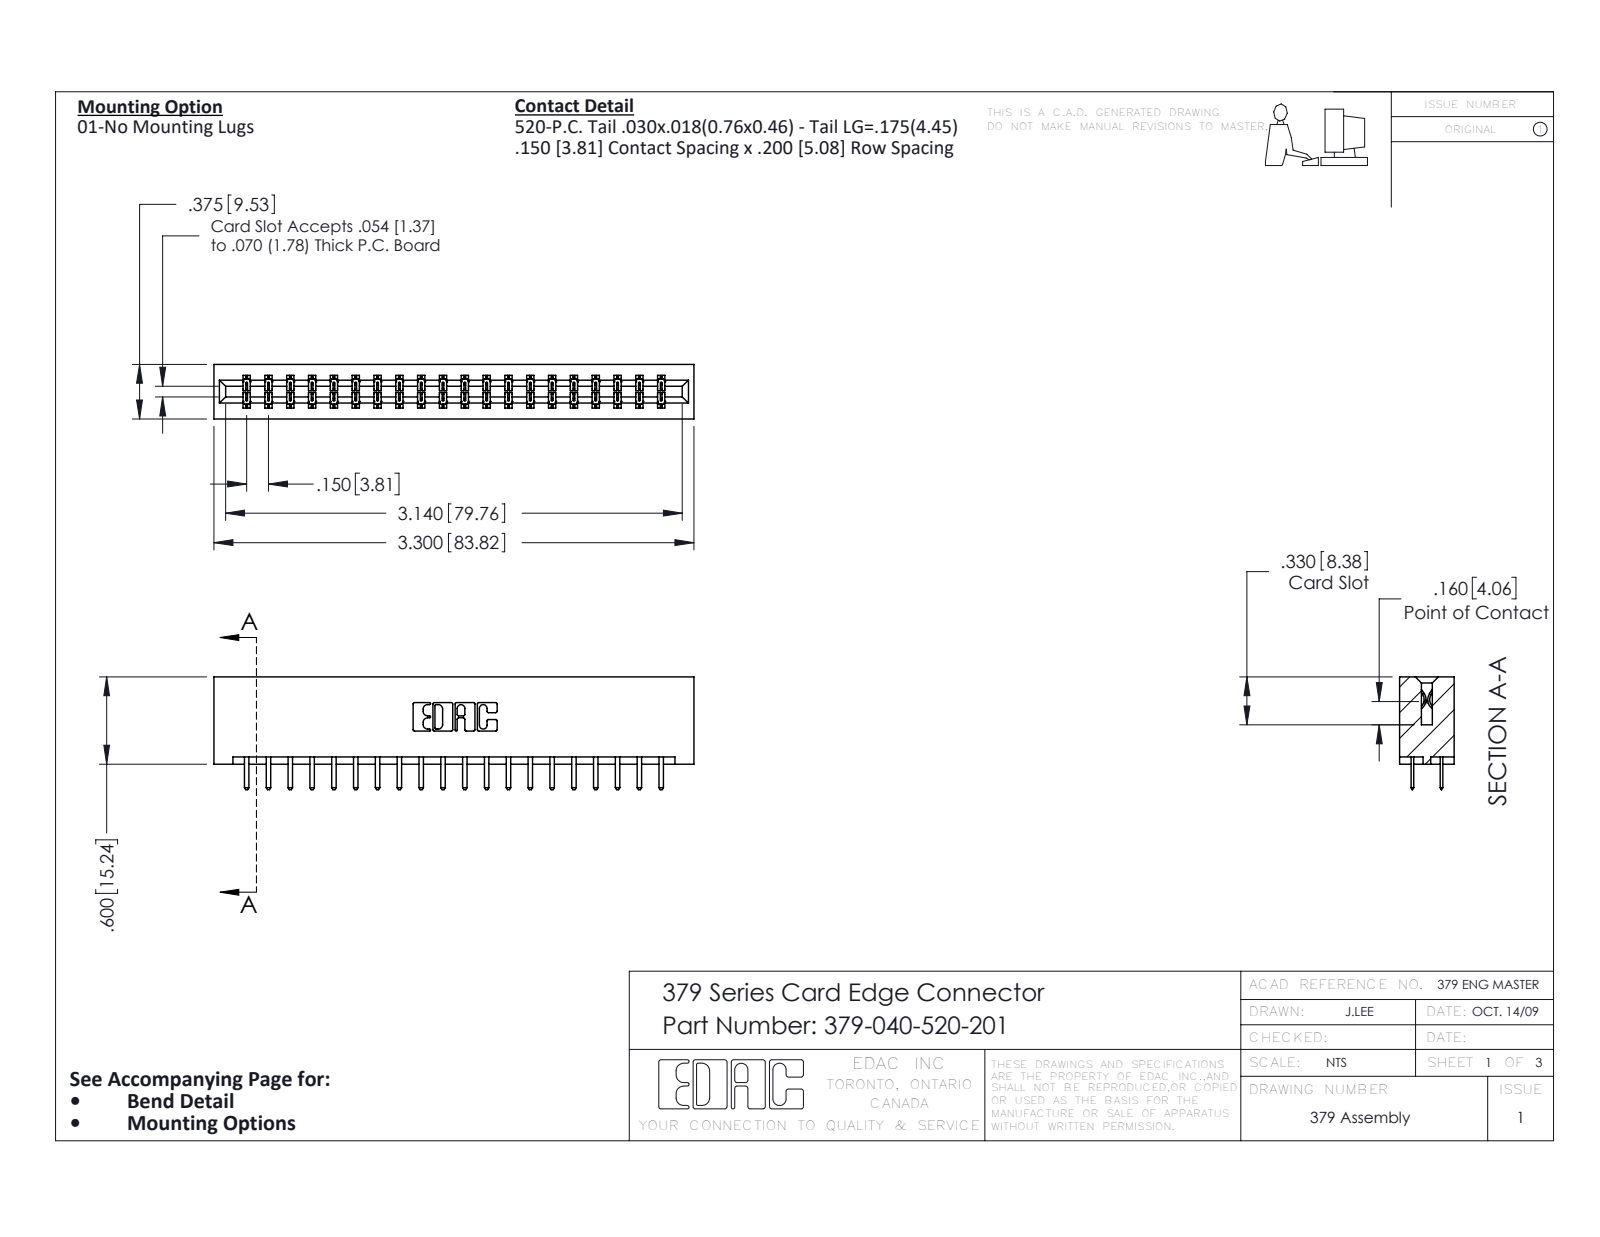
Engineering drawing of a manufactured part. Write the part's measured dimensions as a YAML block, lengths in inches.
part_name: "345-292-001_345-293-120; 379-040-520-201; 379 Part_Lugless"
step_written_by: "SolidWorks 2016 (CONFIG_CONTROL_DESIGN)"
units: inches
bodies: {solids: 41, faces: 2346, planar: 1586, cylindrical: 760, other: 0}
overall_size: [3.3, 0.775, 0.375]
volume: 0.572
surface_area: 16
partial_cylinders:
  - {radius: 0.006, count: 60}
  - {radius: 0.01, count: 44}
  - {radius: 0.01, count: 22}
  - {radius: 0.007, count: 6}
  - {radius: 0.031, count: 6}
  - {radius: 0.026, count: 3}
  - {radius: 0.014, count: 2}
  - {radius: 0.022, count: 2}
face_to_face_distances: [0.3, 0.075, 0.375, 0.2, 0.1, 0.15, 0.225, 0.55, 0.6, 0.05]
